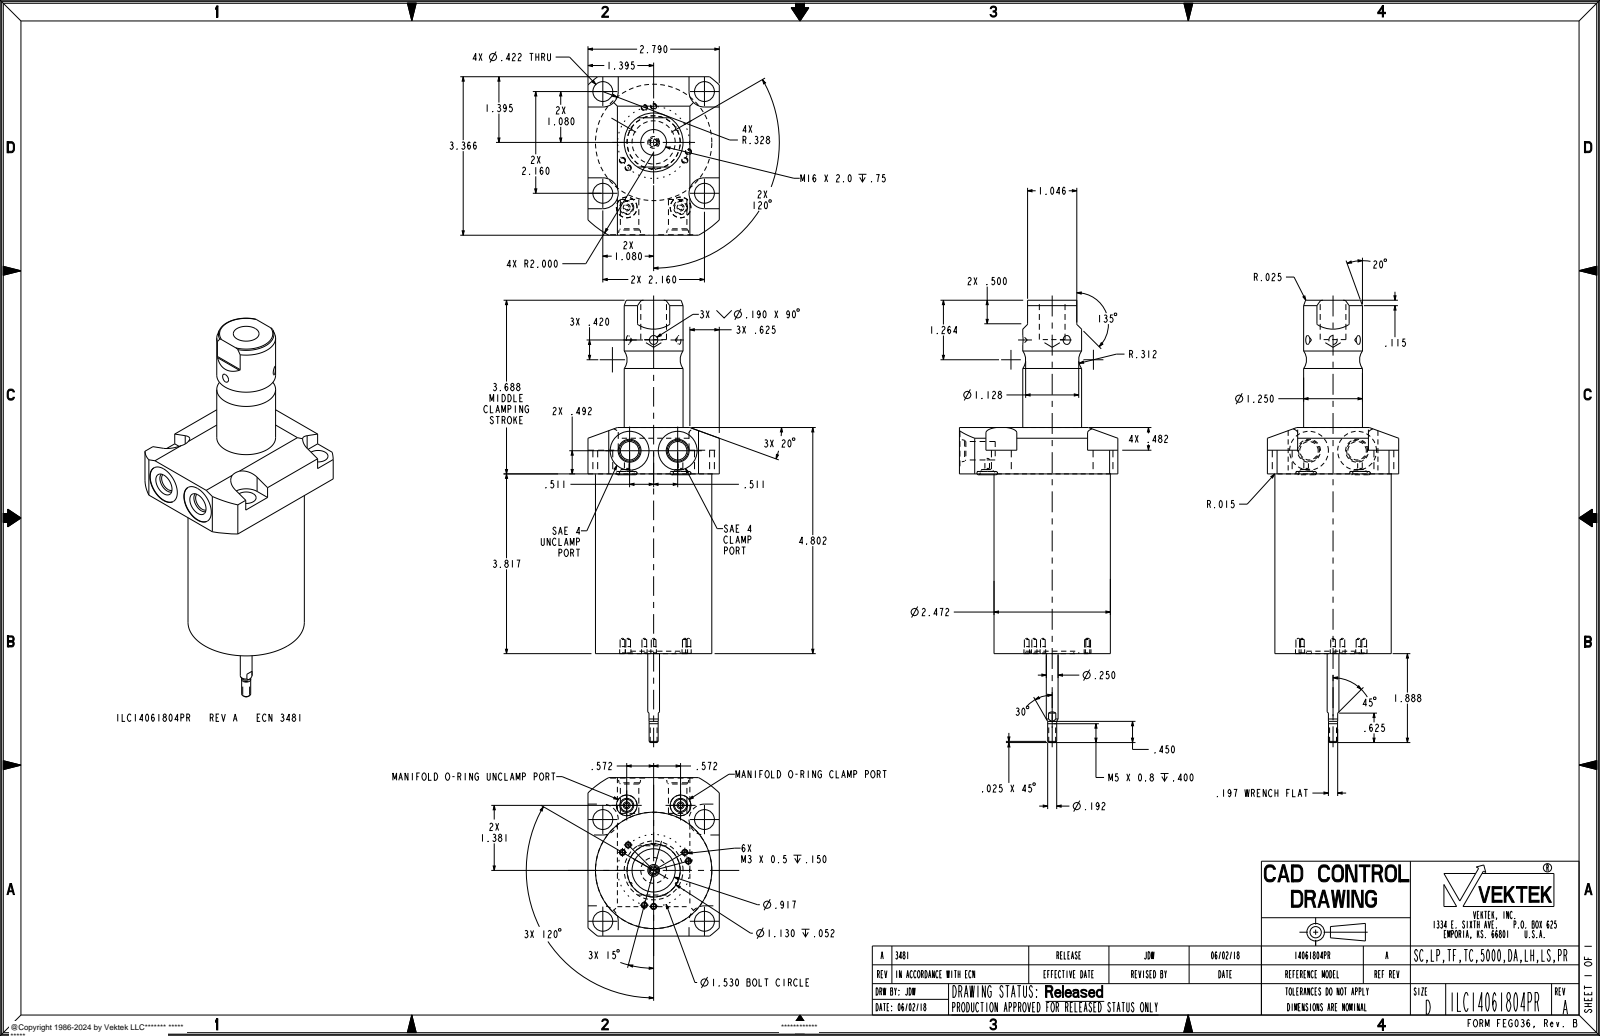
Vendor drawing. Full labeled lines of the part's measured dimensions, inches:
Part name (STEP PRODUCT): ILC14061804PR
STEP written by: PRO/ENGINEER BY PARAMETRIC TECHNOLOGY CORPORATION, 2013320 (AUTOMOTIVE_DESIGN)
Units: inches
Bodies: 3 solids, 195 faces (51 planar, 80 cylindrical, 64 other)
Overall size (bounding box): 9.391 × 3.366 × 2.79
Volume: 28.85 in³ · Surface area: 77.72 in²
Round holes (diameter × count): ⌀0.1 ×6, ⌀0.422 ×4, ⌀0.098 ×2, ⌀0.256 ×2, ⌀0.392 ×2, ⌀0.438 ×2, ⌀0.825 ×2, ⌀0.546 ×1, ⌀1.13 ×1
Round bosses / shafts (diameter × count): ⌀0.118 ×6, ⌀2.472 ×1, ⌀1.25 ×1, ⌀0.917 ×1, ⌀0.25 ×1, ⌀0.192 ×1, ⌀0.147 ×1
Partial cylindrical surfaces — rounded edges, fillets, slot ends (radius × count): R0.328 ×4, R0.03 ×2, R2 ×1
Main face-to-face distances: 3.817, 4.802, 0.985, 2.79, 4.32, 0.503, 0.482, 3.366, 7.505, 3.688
Hole centre spacings: 1.325, 0.765, 1.527, 2.16, 0.2, 0.591, 0.765, 0.813
